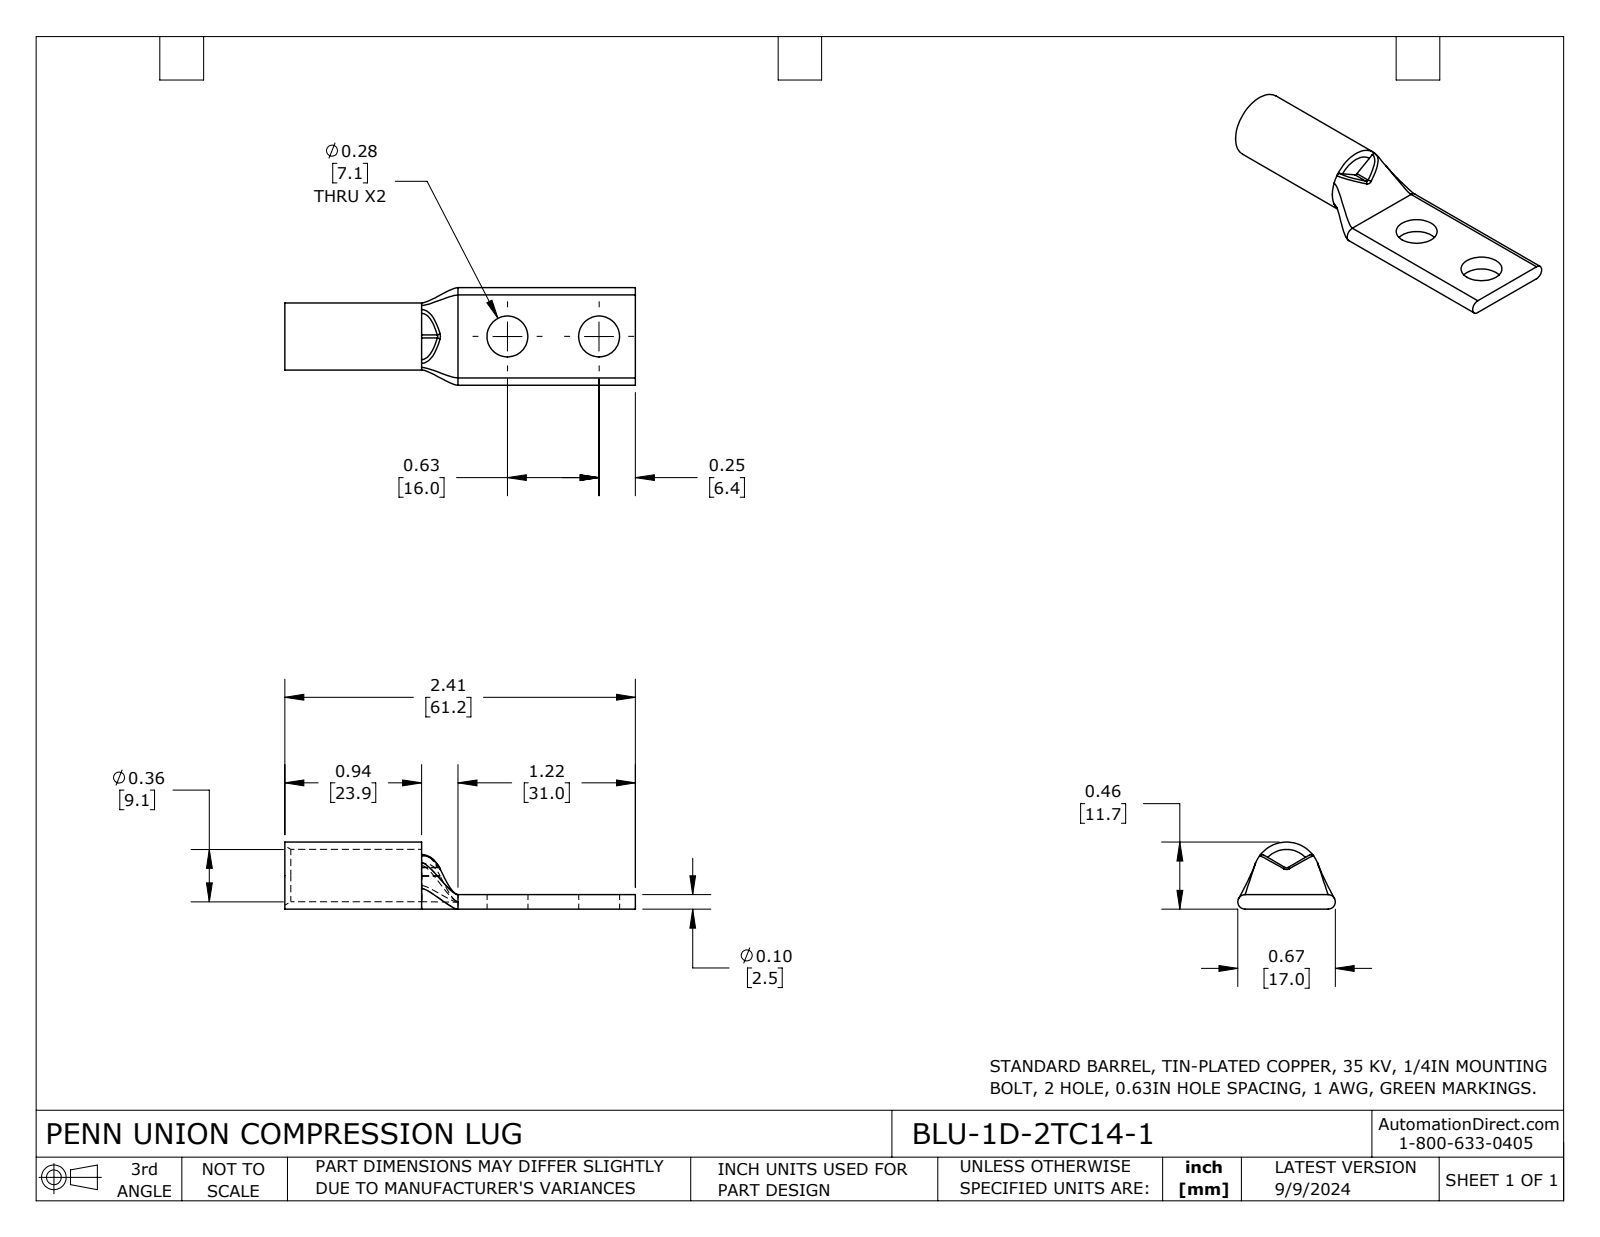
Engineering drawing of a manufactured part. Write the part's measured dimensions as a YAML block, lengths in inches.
part_name: "BLU-1D-2TC14-1"
step_written_by: "SolidWorks 2023 (CONFIG_CONTROL_DESIGN)"
units: inches
bodies: {solids: 1, faces: 37, planar: 11, cylindrical: 13, other: 13}
overall_size: [2.41, 0.67, 0.461]
volume: 0.143
surface_area: 5.038
round_holes:
  - {diameter: 0.281, count: 2}
  - {diameter: 0.36, count: 1}
round_bosses_or_shafts:
  - {diameter: 0.461, count: 1}
partial_cylinders:
  - {radius: 0.02, count: 2}
  - {radius: 0.05, count: 2}
face_to_face_distances: [0.1, 2.41, 0.94, 1.47, 0.05, 1.19, 0.25, 1.22]
hole_center_spacings: [0.63]
